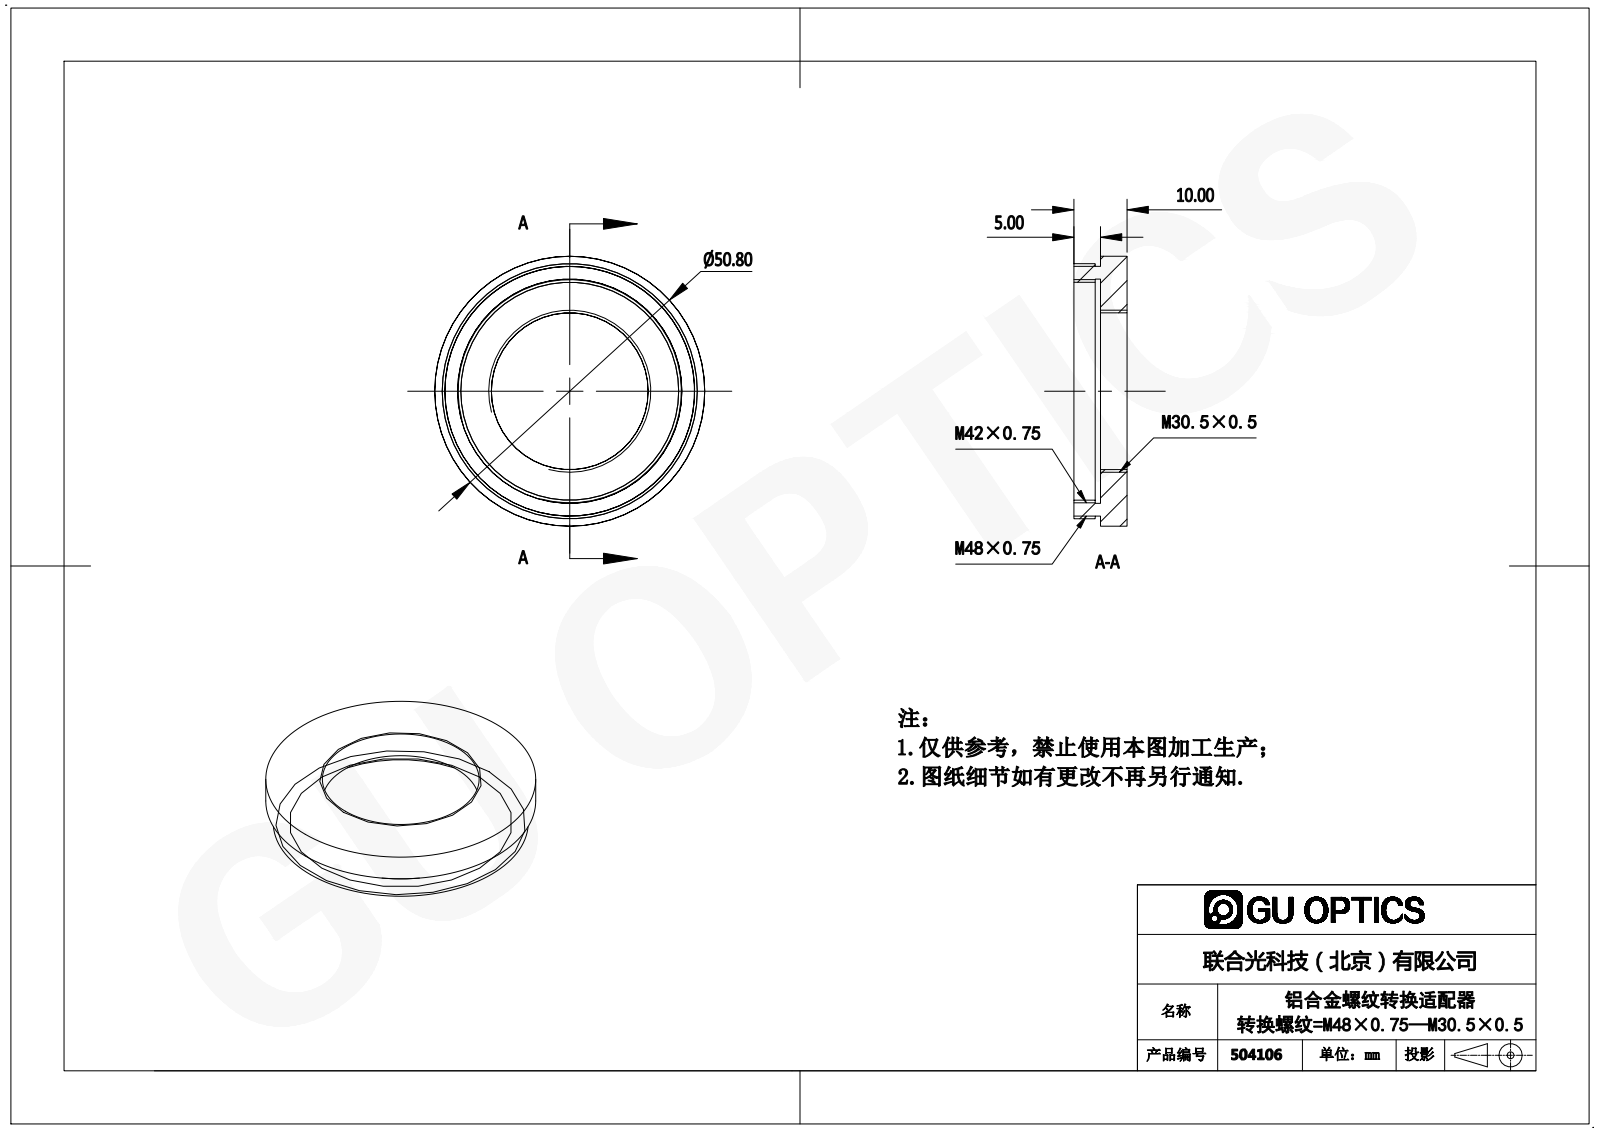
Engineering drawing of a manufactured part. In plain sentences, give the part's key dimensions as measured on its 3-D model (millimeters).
The part is named "504106". Its 3-D file was written by "SolidWorks 2016 (AUTOMOTIVE_DESIGN)". It is 1 solid with 18 faces: 6 planar, 12 cylindrical and 0 other. Overall it measures 50.8 by 50.8 by 10 millimeters. Its volume is 9 010 cubic millimeters and its surface area 5 653 square millimeters. Round holes: 1 of diameter 29.5, 1 of diameter 41, 1 of diameter 42.2. Round bosses or shafts: 1 of diameter 50.8, 1 of diameter 48, 1 of diameter 47. The main face-to-face distances are 5, 10, 4, 1, 6.
